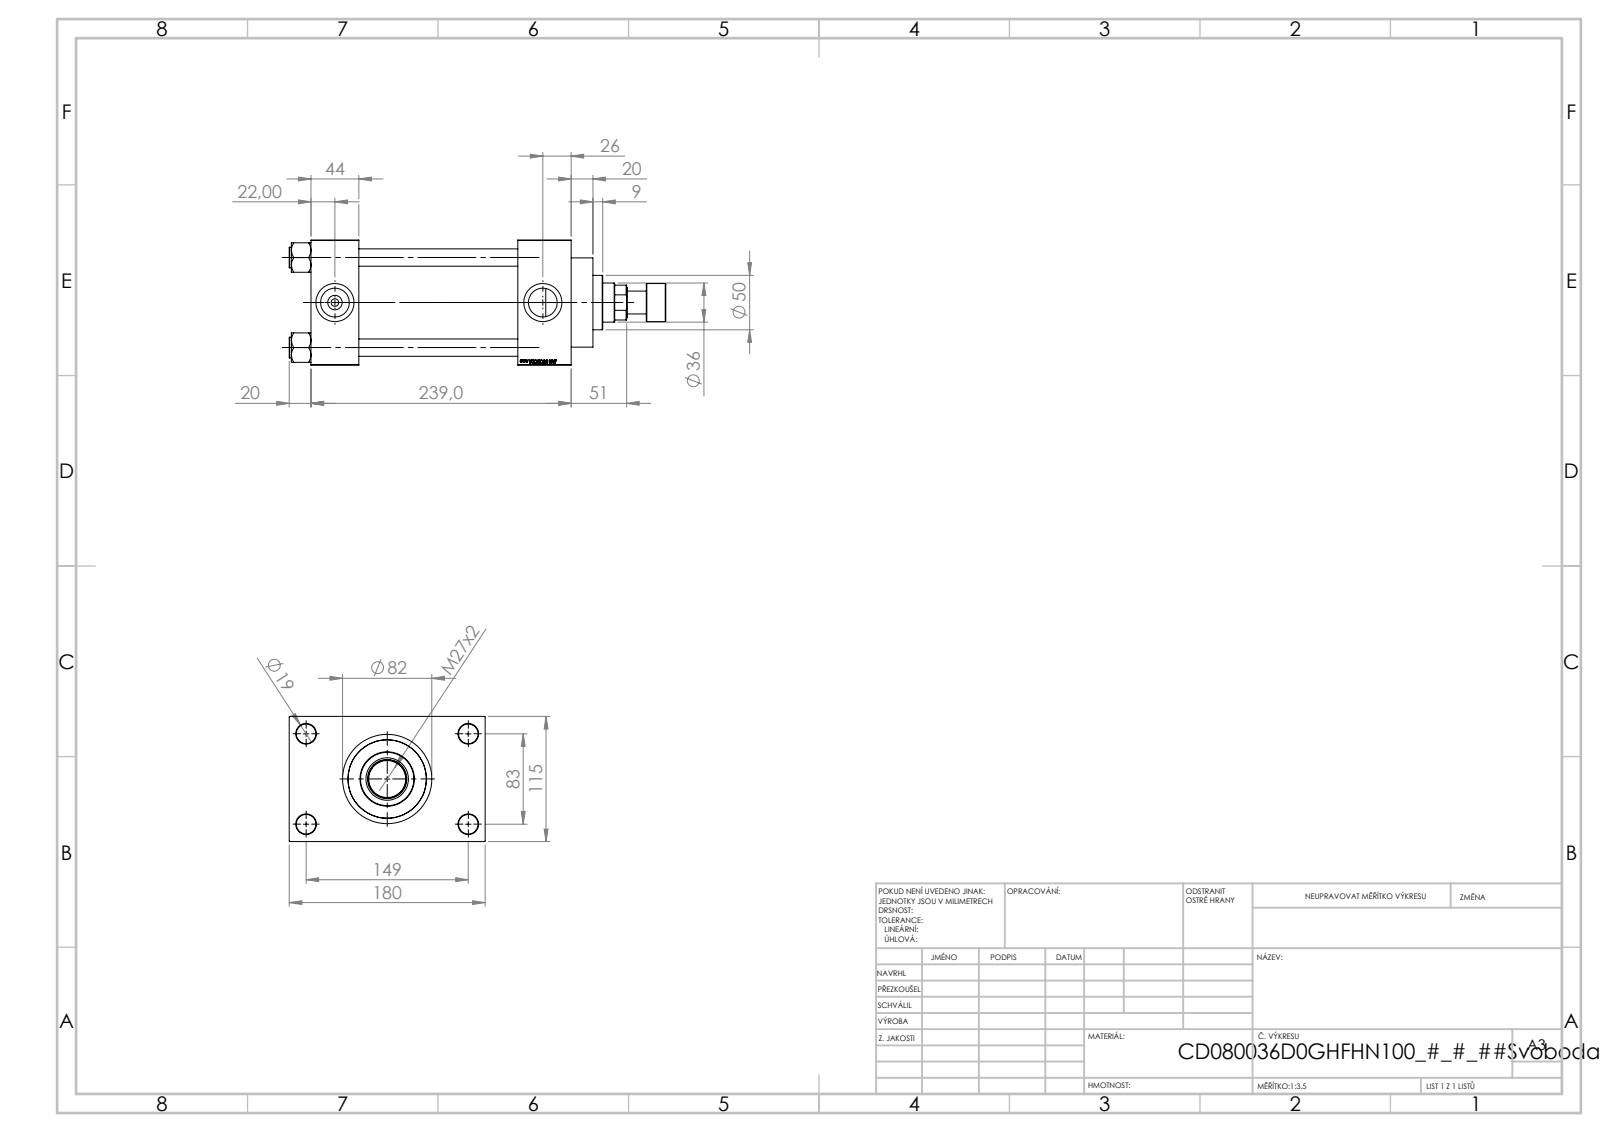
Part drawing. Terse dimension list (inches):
name: V215CD_D_TYCINKA; V215CR_ROD_END_F; V215CD_NUT_M5_D; V215CD_VCP_D (+2 more)
written by: SolidWorks 2019 (CONFIG_CONTROL_DESIGN)
unit: in
bodies: 12 solids, 1165 faces (549 planar, 92 cylindrical, 524 other)
size: 13.622 × 7.087 × 4.528
volume: 134.9 in³; area: 572 in²
holes: 4× ⌀0.63, 4× ⌀0.709, 2× ⌀0.276, 2× ⌀1.041, 2× ⌀1.378, 1× ⌀1.004, 1× ⌀1.417, 1× ⌀1.535, 1× ⌀2.402, 1× ⌀2.835, 1× ⌀3.15
bosses: 4× ⌀0.748, 1× ⌀3.386, 1× ⌀3.228, 1× ⌀1.969, 1× ⌀1.378, 1× ⌀0.827
face distances: 4.528, 5.748, 1.929, 7.677, 1.732, 7.48, 9.409, 1.28, 5.807, 3.937
hole spacings: 1.305, 2.302, 3.256, 3.357, 3.513, 4.561, 5.607, 3.268
